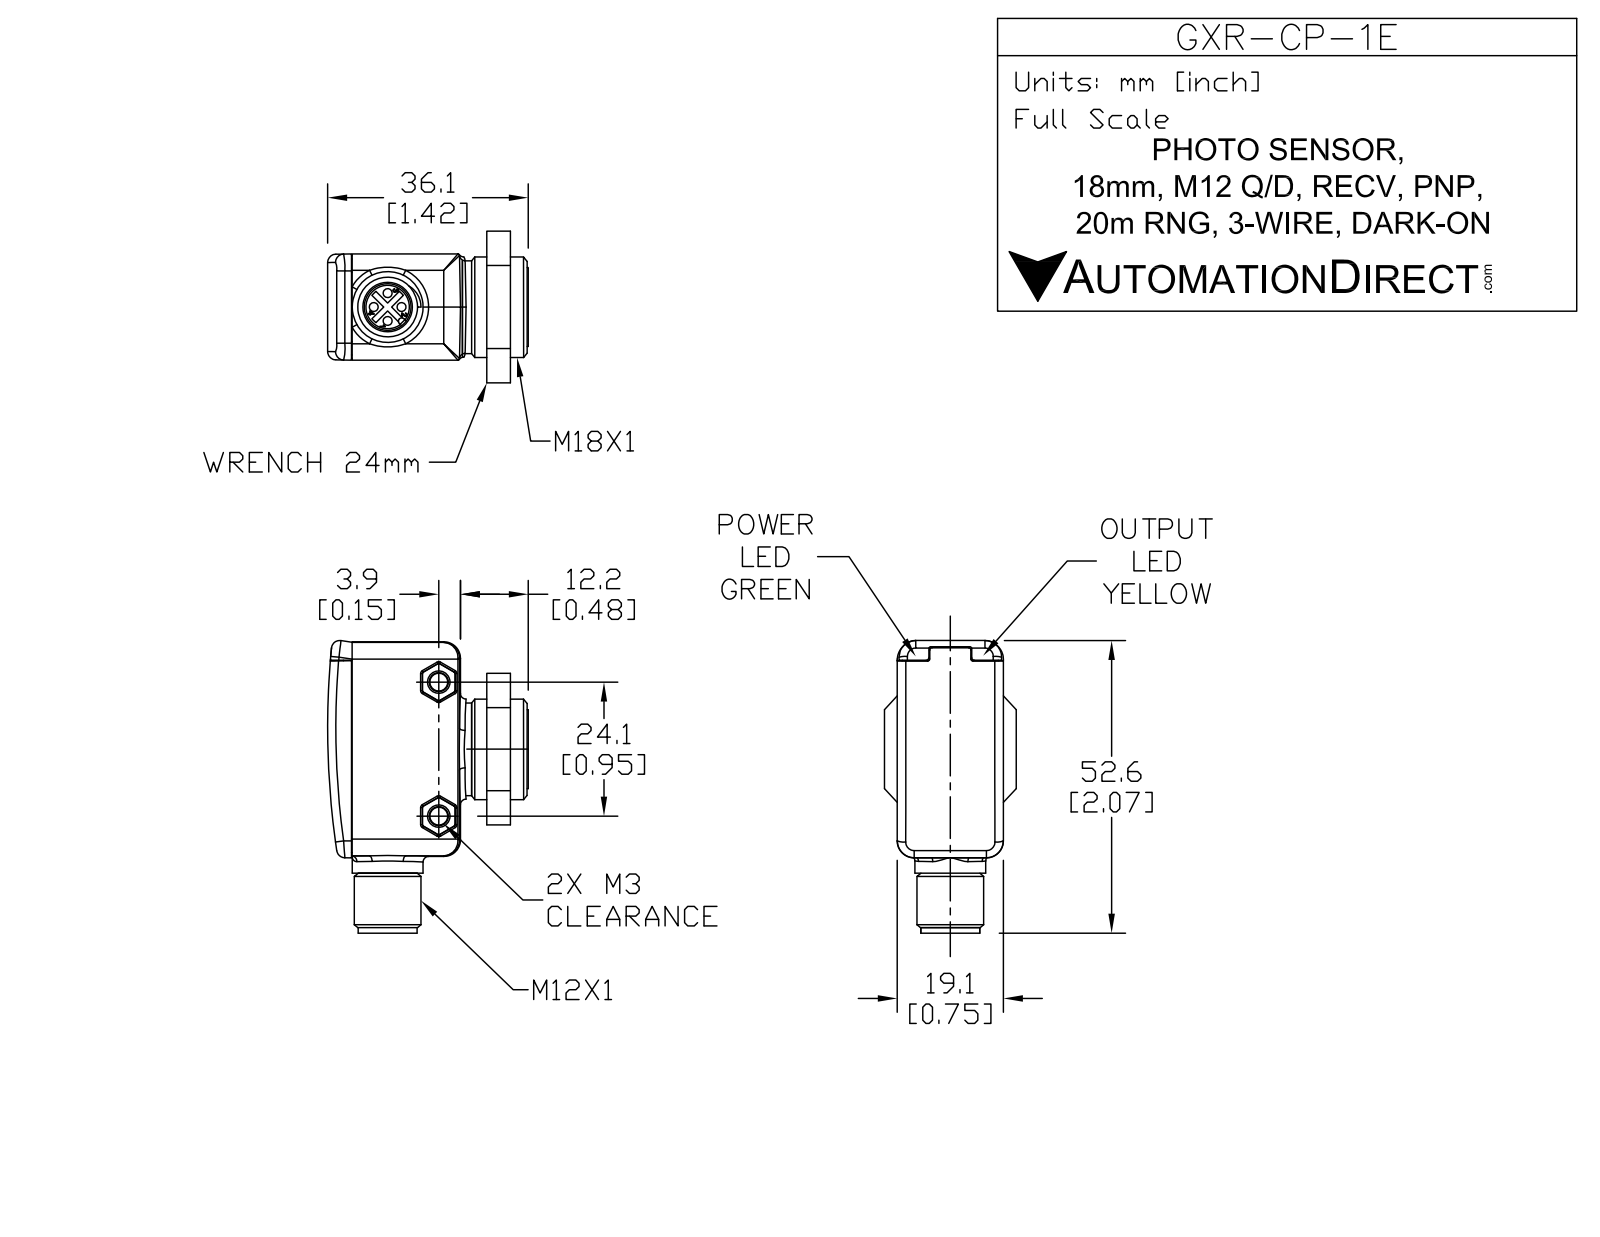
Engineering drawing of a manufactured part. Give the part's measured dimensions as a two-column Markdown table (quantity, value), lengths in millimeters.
| quantity | value |
| --- | --- |
| part name | GXR-CP-1E |
| STEP written by | SolidWorks 2013 (AUTOMOTIVE_DESIGN) |
| units | millimeters |
| bodies | 1 solid, 107 faces (60 planar, 33 cylindrical, 14 other) |
| overall size | 52.66 × 36.1 × 23.85 |
| volume | 21 253 mm³ |
| surface area | 6 452 mm² |
| round holes (diameter × count) | 3.2 × 2, 8.36 × 1 |
| round bosses / shafts (diameter × count) | 18 × 1, 17.5 × 1, 14.2 × 1, 12.68 × 1, 11.55 × 1, 10.6 × 1 |
| partial cylindrical surfaces (radius × count) | 1.5 × 8, 1 × 4, 139.57 × 1 |
| main face-to-face distances | 19.1, 7.2, 2.12, 9.32, 19.2, 5, 2.88, 12.2, 38.8, 5.95 |
| hole center spacings | 24.1 |
